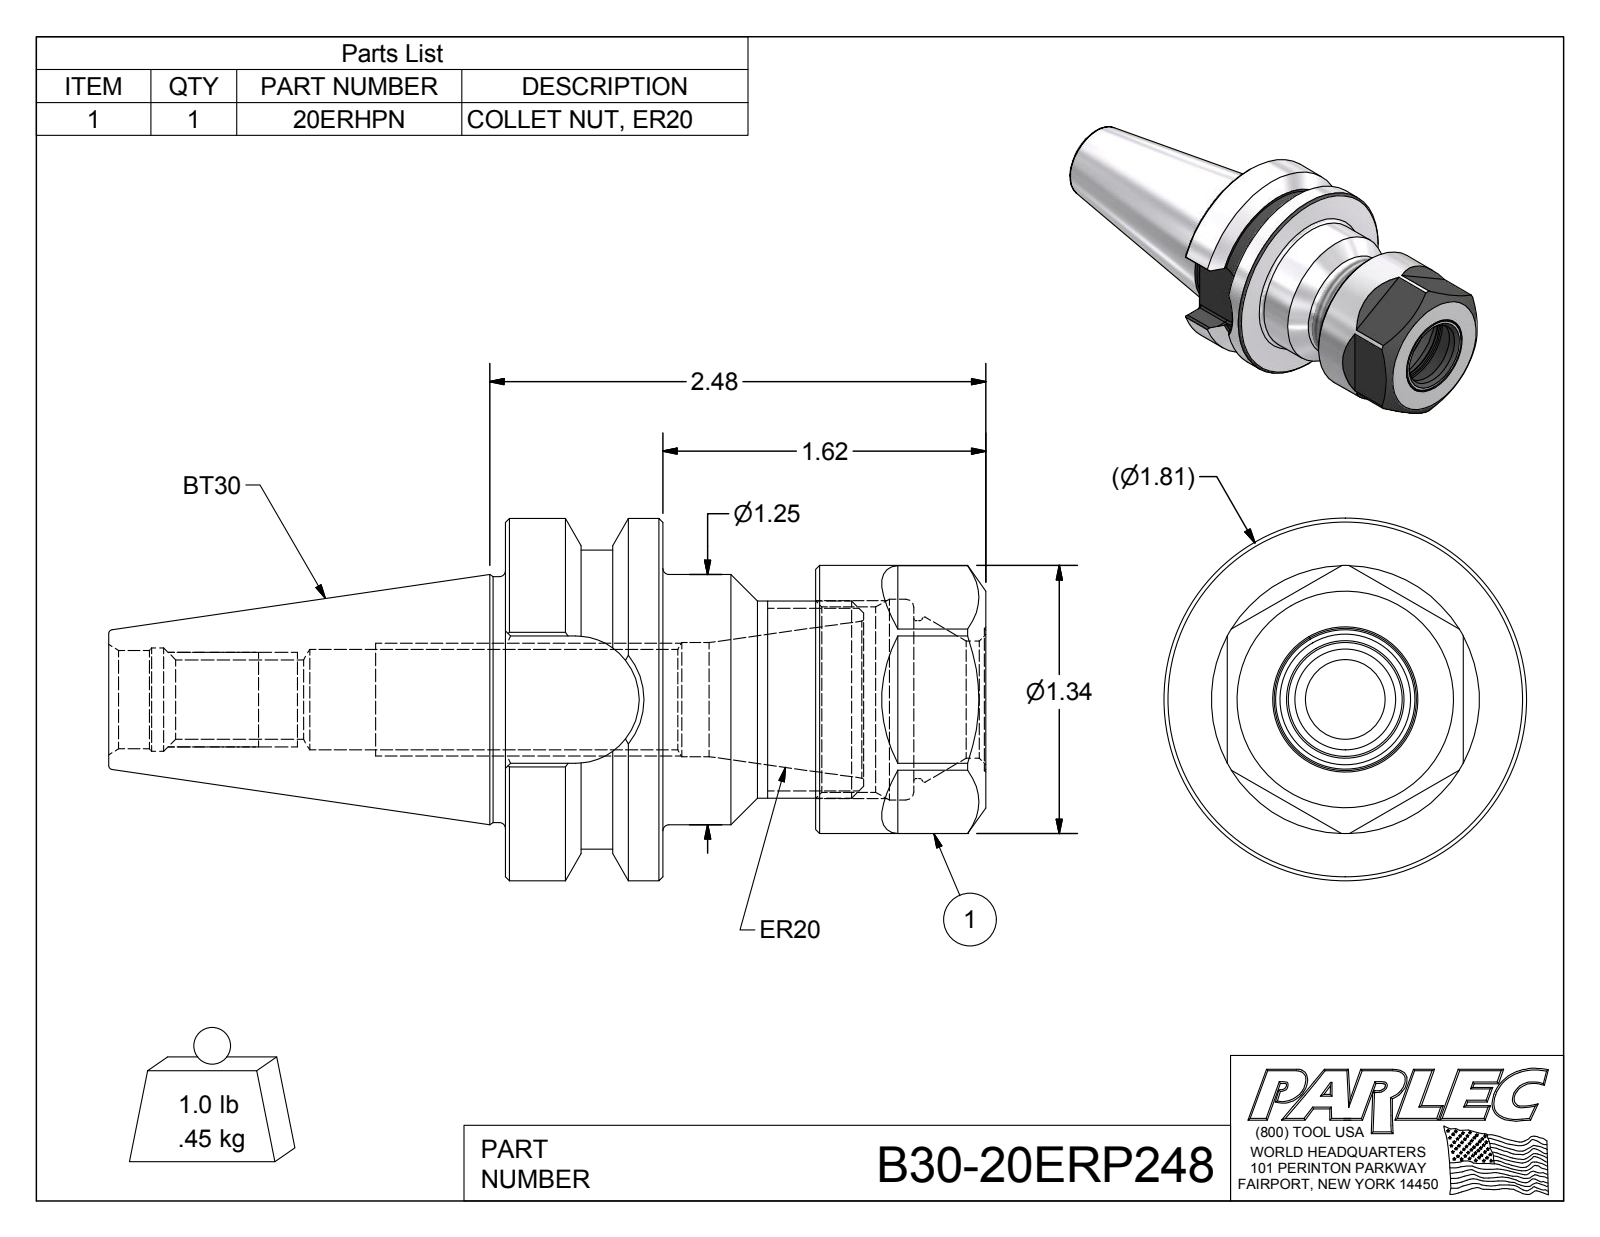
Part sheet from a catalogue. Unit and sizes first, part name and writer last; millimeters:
Units: millimetres
Overall size (bounding box): 111.4 × 46 × 46
Round holes (diameter × count): ⌀10.11 ×1, ⌀12.51 ×1, ⌀12.75 ×1, ⌀13.12 ×1, ⌀14.48 ×1, ⌀14.91 ×1, ⌀20.07 ×1, ⌀23.52 ×1, ⌀25.53 ×1
Round bosses / shafts (diameter × count): ⌀46 ×1, ⌀34.04 ×1, ⌀31.75 ×1, ⌀31.24 ×1, ⌀25 ×1
Partial cylindrical surfaces — rounded edges, fillets, slot ends (radius × count): R0.51 ×8, R8.09 ×1, R19 ×1
Main face-to-face distances: 19.99, 29.98, 39.42, 19.43, 61.01, 41.02, 21.59, 1.31, 31.29, 32.6
Volume: 64 842 mm³ · Surface area: 20 518 mm²
Bodies: 2 solids, 104 faces (39 planar, 28 cylindrical, 37 other)
Part name (STEP PRODUCT): B30-20ER236-1; 20ERHPN; B30-20ERP248
STEP written by: Autodesk Inventor 2016 (AUTOMOTIVE_DESIGN)
